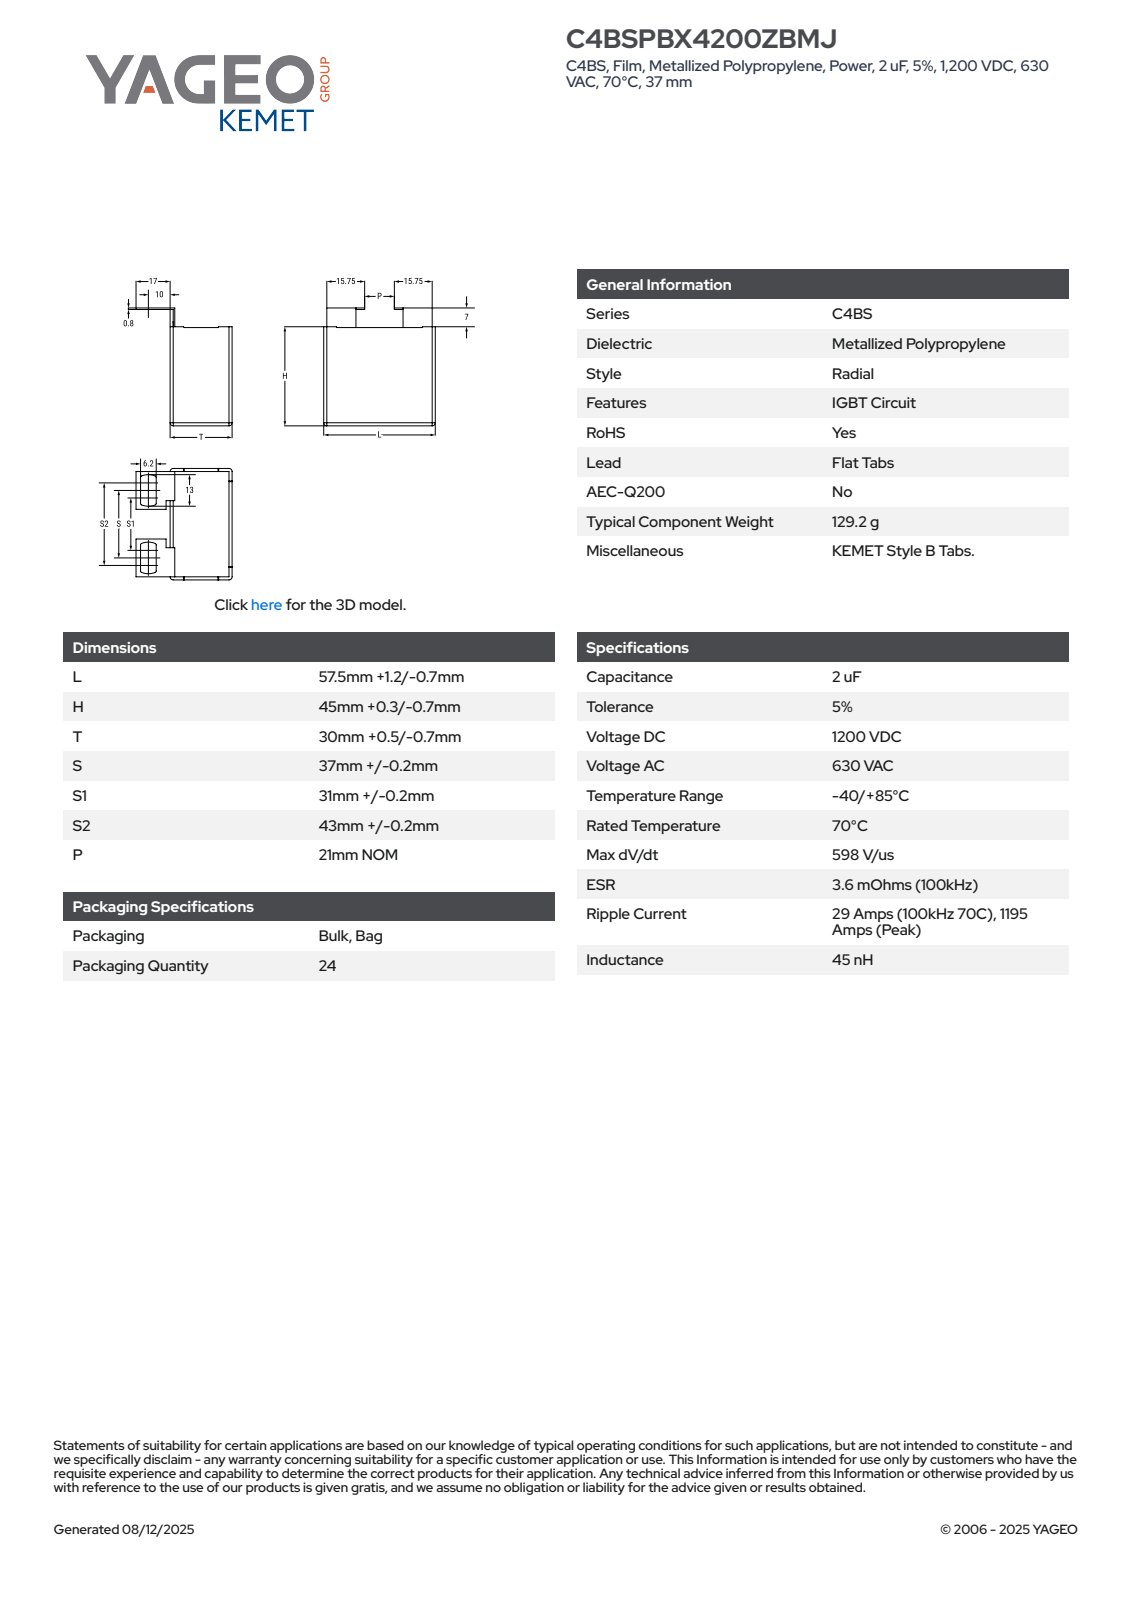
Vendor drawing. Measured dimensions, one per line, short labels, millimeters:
name: CFP_C4BB_57.5X45X30_L58.7H45.3T30.5S37.2
written by: SolidWorks 2014 (AUTOMOTIVE_DESIGN)
unit: mm
bodies: 4 solids, 93 faces (85 planar, 8 cylindrical, 0 other)
size: 58.7 × 52.3 × 47.5
volume: 81 638 mm³; area: 13 353 mm²
rounds: 4× R4.6, 2× R0.2
face distances: 30.5, 45.3, 58.7, 0.8, 7, 52.3, 6.2, 51.5, 28.5, 2
